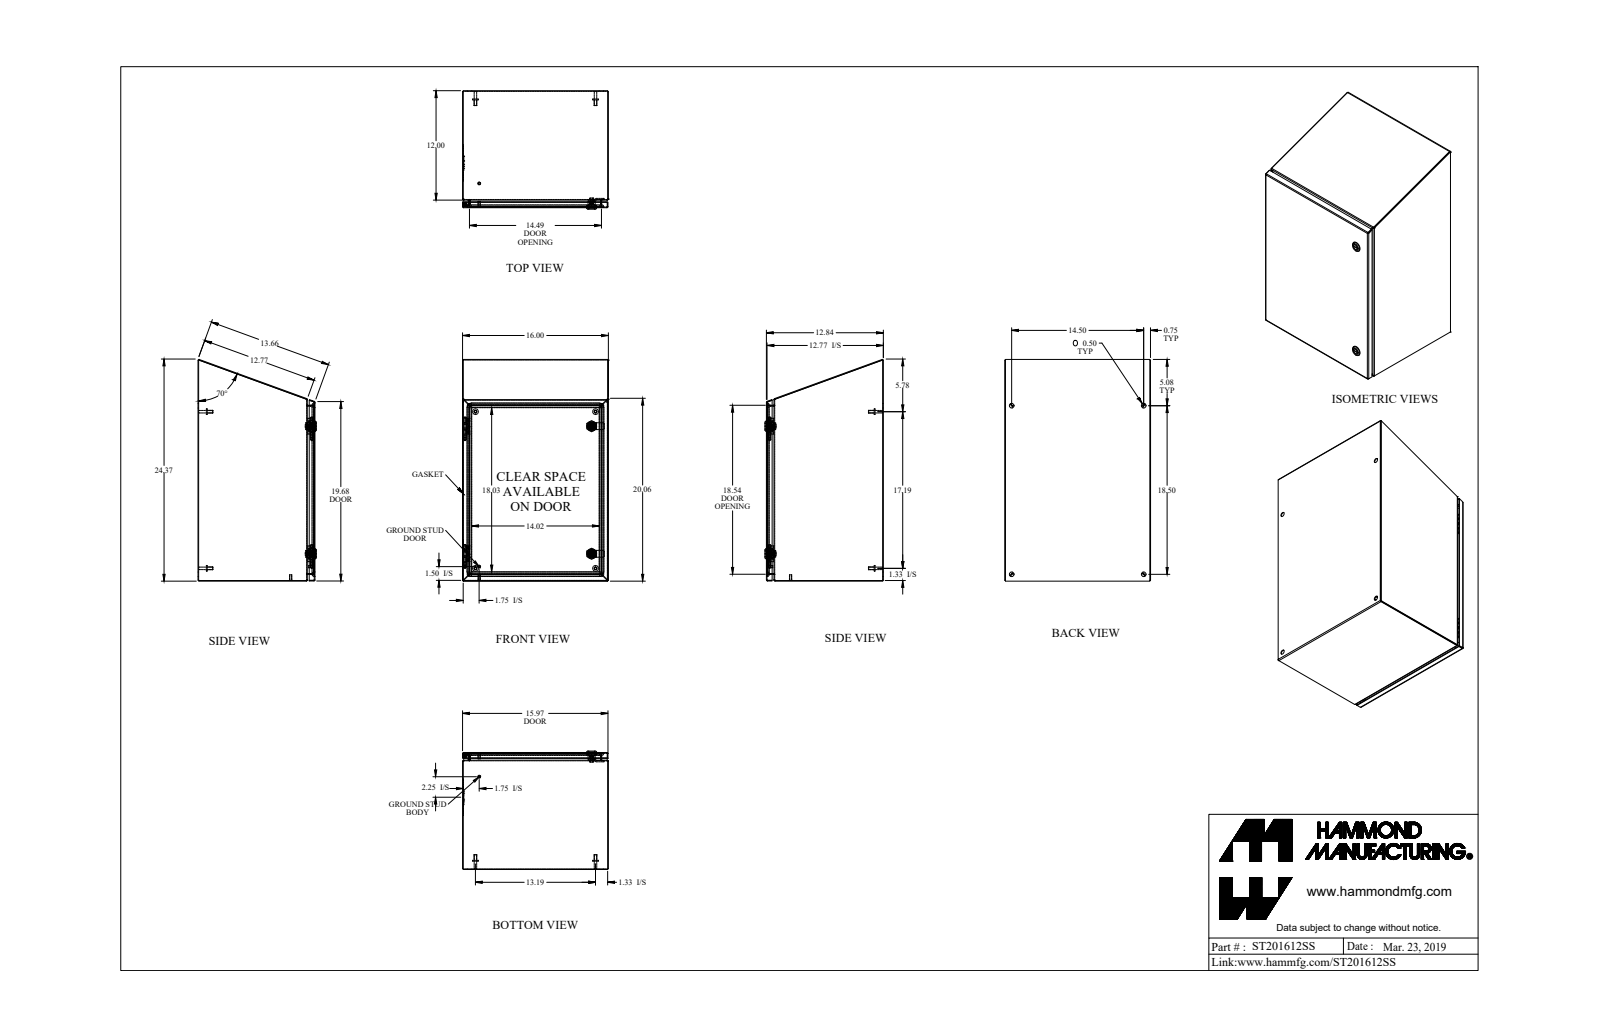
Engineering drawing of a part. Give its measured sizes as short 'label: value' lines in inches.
name: ST201612SS
written by: SolidWorks 2018 (AUTOMOTIVE_DESIGN)
unit: in
bodies: 29 solids, 746 faces (378 planar, 232 cylindrical, 136 other)
size: 24.328 × 16.008 × 12.997
volume: 134.5 in³; area: 3 716 in²
holes: 6× ⌀0.5, 2× ⌀0.197, 2× ⌀0.387, 2× ⌀0.63, 2× ⌀0.768, 1× ⌀0.172, 1× ⌀0.24, 1× ⌀0.242
bosses: 6× ⌀0.625, 6× ⌀0.313, 4× ⌀0.275, 2× ⌀1.1, 2× ⌀0.785, 2× ⌀0.525, 2× ⌀0.25, 2× ⌀0.236
rounds: 18× R0.036, 18× R0.108, 6× R0.188, 4× R0.006, 4× R0.062, 4× R0.125, 4× R0.25, 4× R0.499
face distances: 0.072, 12.765, 15.928, 12.693, 12.837, 15.856, 16, 11.928, 0.837, 0.909
hole spacings: 14.5, 18.5, 23.506, 2.497, 2.499, 13.602, 13.603, 14
